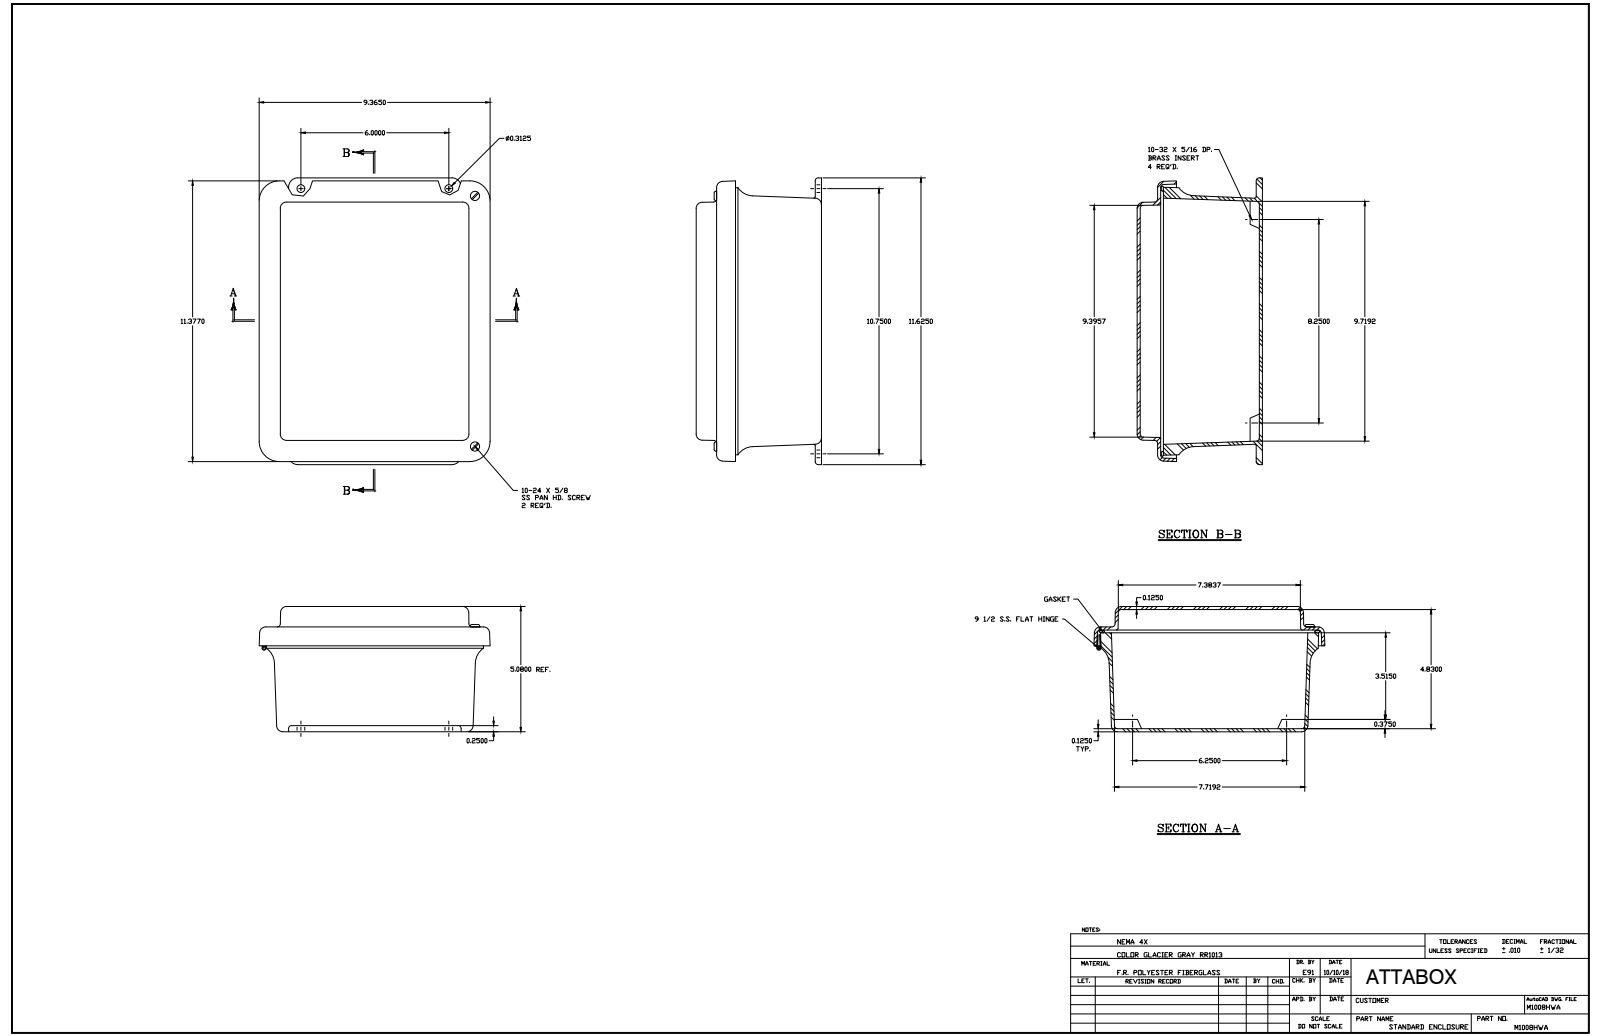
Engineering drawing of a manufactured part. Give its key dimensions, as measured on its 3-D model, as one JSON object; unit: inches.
{"part_name": "M1008HWA", "step_written_by": "SolidWorks 2018 (AUTOMOTIVE_DESIGN)", "units": "inches", "bodies": {"solids": 22, "faces": 809, "planar": 269, "cylindrical": 307, "other": 233}, "overall_size": [11.625, 9.393, 5.064], "volume_in3": 62.09, "surface_area_in2": 851.9, "round_holes": [[0.131, 8], [0.14, 8], [0.152, 5], [0.156, 4], [0.218, 4], [0.145, 2], [0.085, 1], [0.085, 1]], "round_bosses_or_shafts": [[0.25, 8], [0.27, 6], [0.125, 4], [0.125, 4], [0.19, 2], [0.156, 2], [0.155, 1], [0.155, 1]], "partial_cylinders_radius": [[0.125, 24], [0.031, 20], [0.25, 12], [0.2, 6], [0.375, 4], [0.75, 4], [0.063, 2]], "face_to_face_distances": [0.125, 0.125, 4.814, 4.939, 5.064, 4.939, 0.829, 3.985, 4.109, 0.954], "hole_center_spacings": [6, 3, 0.25, 2.5, 2.75, 6.25, 1.337, 3.25]}
